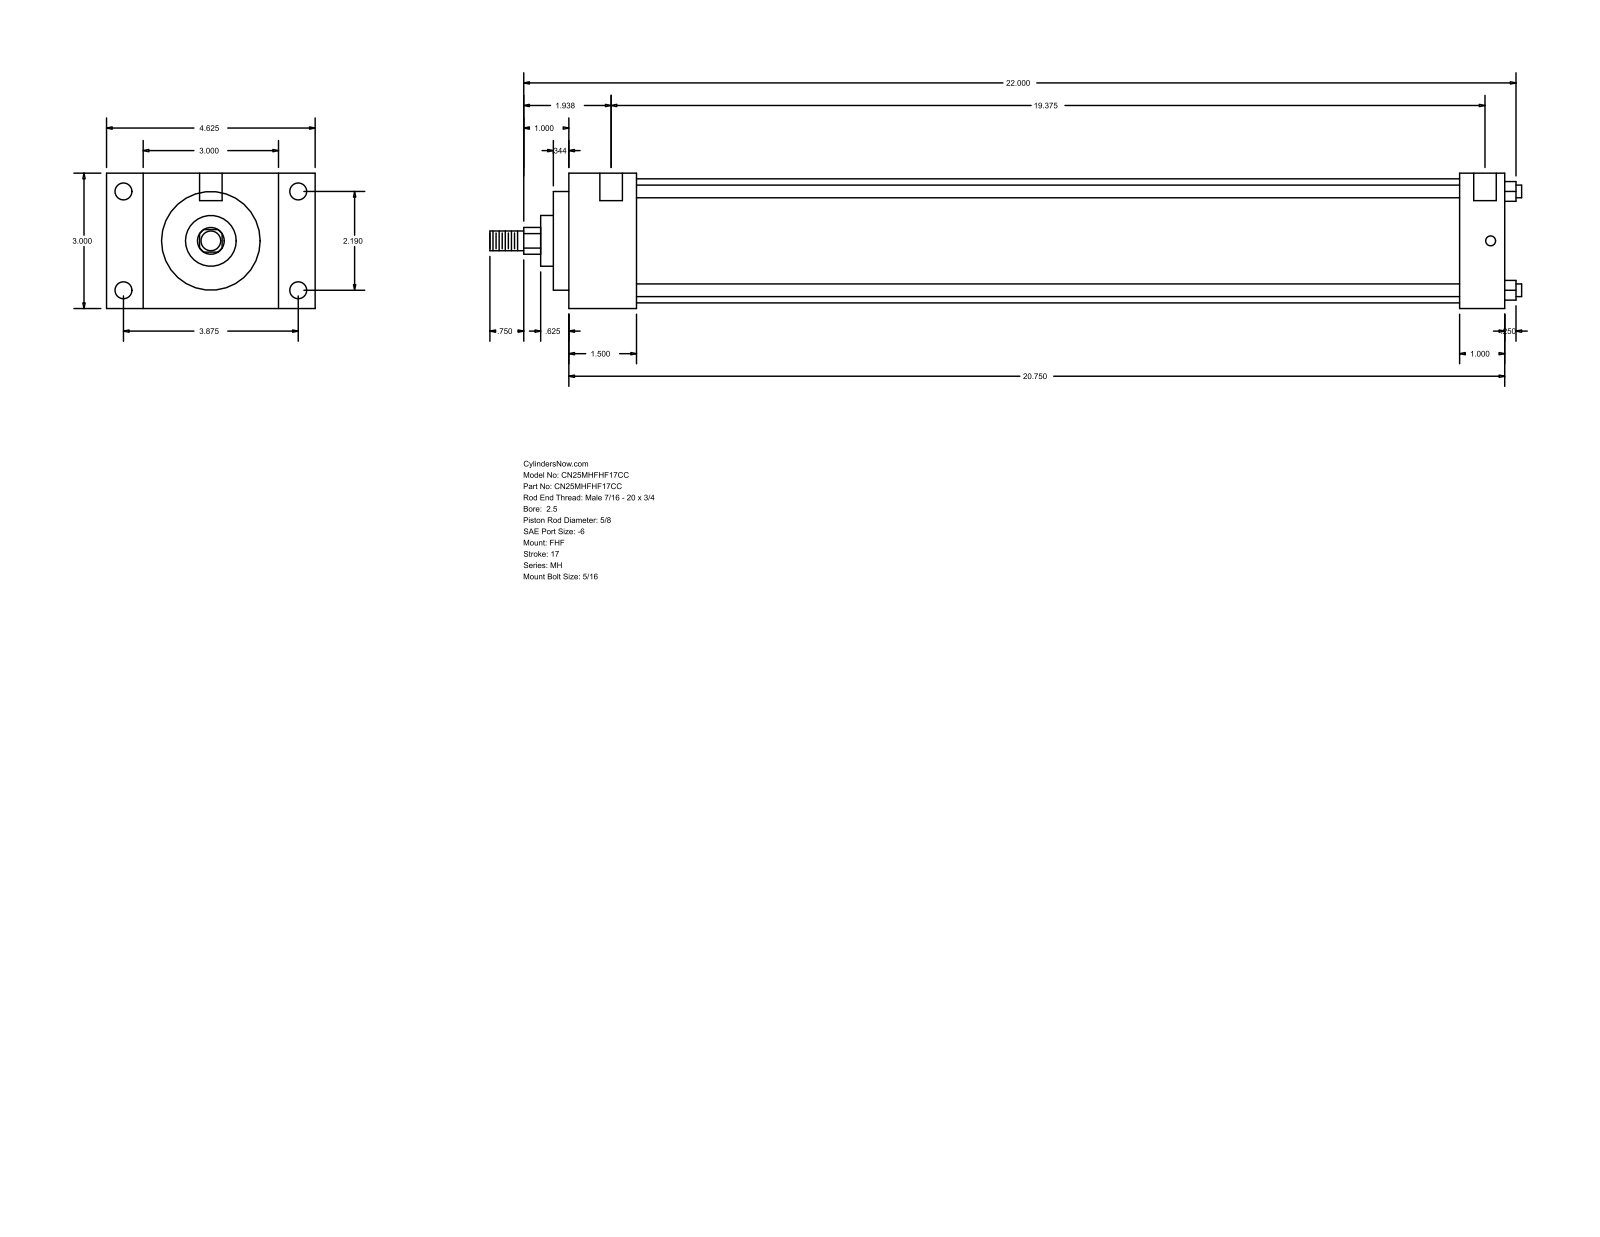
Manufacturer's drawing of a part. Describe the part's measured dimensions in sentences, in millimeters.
The part is named "MH_FHF__0250_0.625". Its 3-D file was written by "GSSL Pune (CONFIG_CONTROL_DESIGN)". It is 0 solids with 90 faces: 61 planar, 29 cylindrical and 0 other. Overall it measures 581.02 by 117.47 by 76.2 millimeters. Round holes: 4 of diameter 5.56, 4 of diameter 9.53, 2 of diameter 12.7. Round bosses or shafts: 4 of diameter 7.14, 1 of diameter 69.85, 1 of diameter 55.55, 1 of diameter 28.57, 1 of diameter 15.88, 1 of diameter 11.11. Partial cylindrical surfaces (rounded edges, fillets, slot ends): 1 of radius 7.54. The main face-to-face distances are 76.2, 527.05, 38.1, 488.95, 20.64, 96.84, 117.48, 25.4, 501.65, 463.55. The hole center spacings are 55.62, 98.42, 113.05, 500.06, 3.17, 4.76, 492.13, 495.3.
